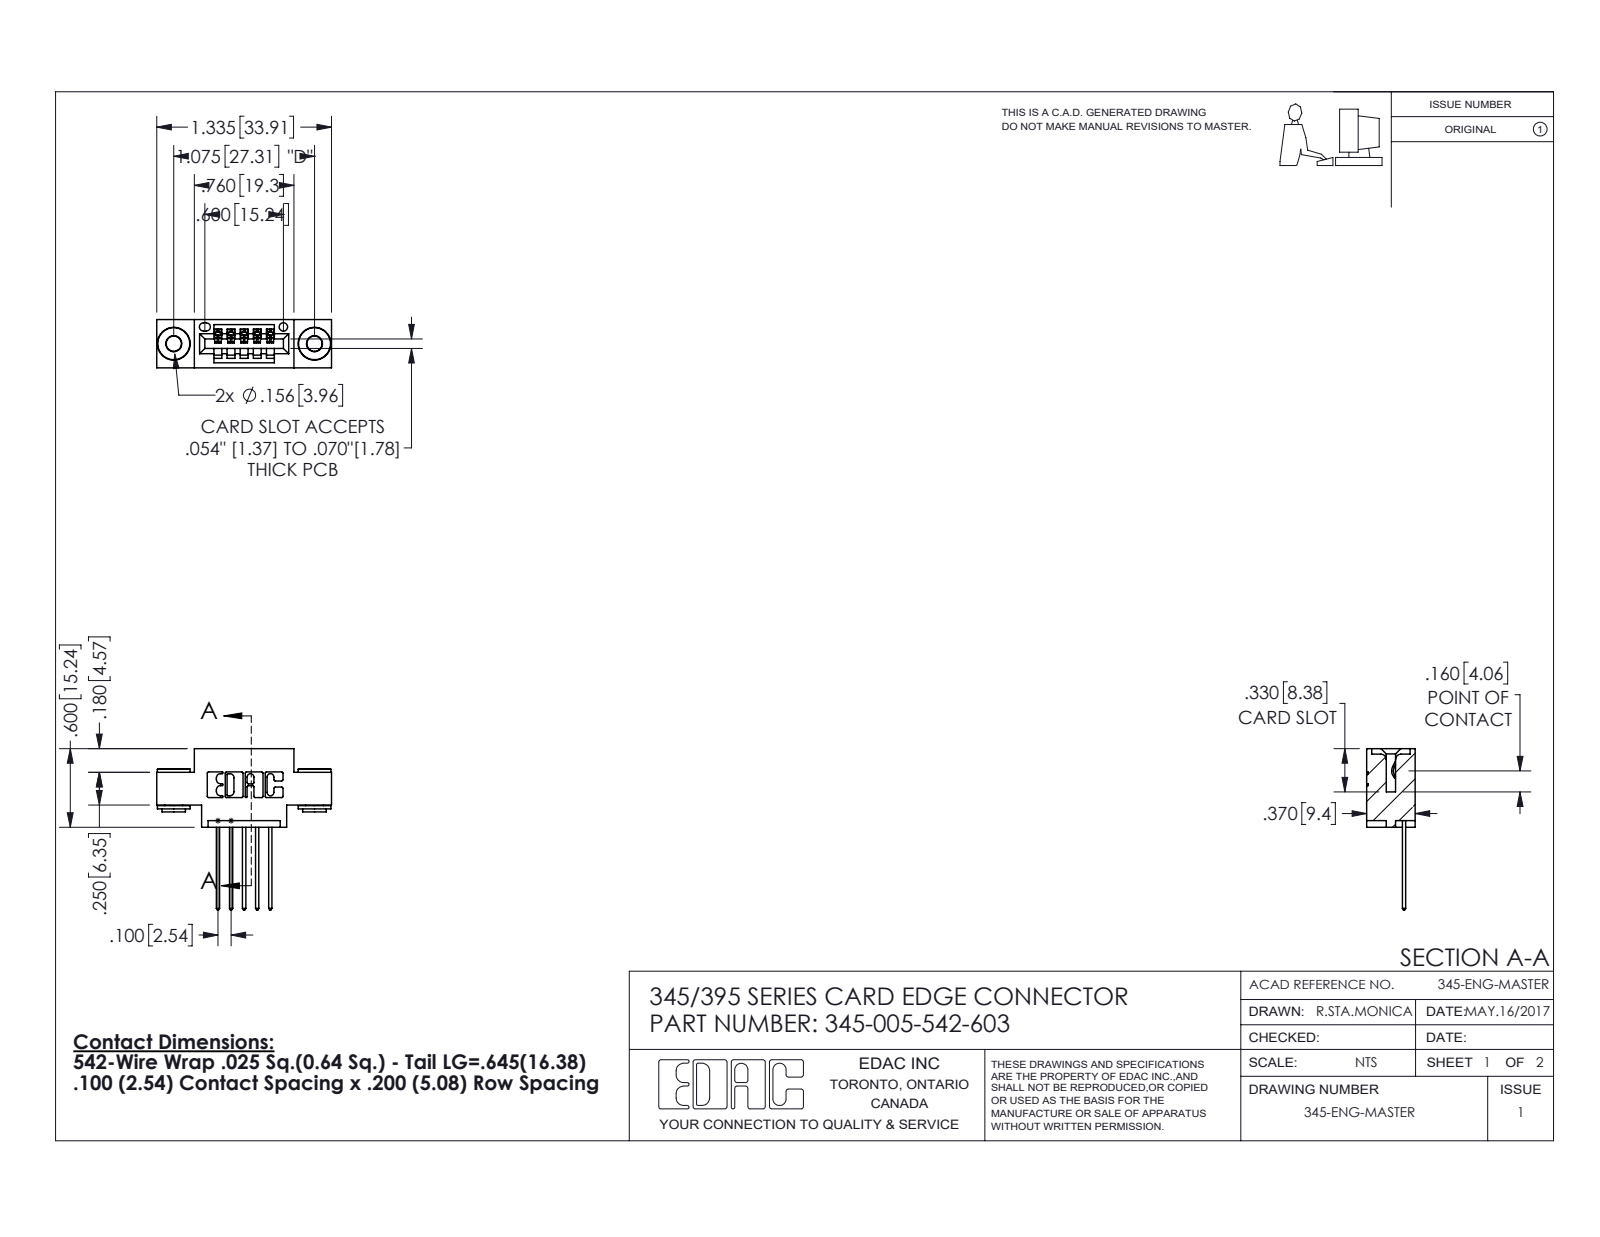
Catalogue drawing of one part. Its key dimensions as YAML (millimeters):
part_name: "345 Part_0.170 Offset - 0.156 Dia-TH; 345-005-542-603; 345-250-002_345-250-002-102; 345-292-001_345-293-142"
step_written_by: "SolidWorks 2016 (CONFIG_CONTROL_DESIGN)"
units: millimeters
bodies: {solids: 8, faces: 458, planar: 294, cylindrical: 156, other: 8}
overall_size: [33.9, 31.3, 9.4]
volume: 2830
surface_area: 3675
round_holes:
  - {diameter: 2.9, count: 2}
  - {diameter: 4, count: 2}
  - {diameter: 1.6, count: 1}
round_bosses_or_shafts:
  - {diameter: 6.4, count: 2}
  - {diameter: 4.6, count: 2}
  - {diameter: 3.5, count: 2}
partial_cylinders:
  - {radius: 0.3, count: 22}
  - {radius: 0.2, count: 10}
  - {radius: 0.3, count: 10}
  - {radius: 0.2, count: 6}
  - {radius: 0.8, count: 6}
  - {radius: 0.7, count: 3}
  - {radius: 0.8, count: 2}
  - {radius: 1, count: 2}
face_to_face_distances: [9.4, 5.1, 2.5, 1.8, 7.6, 0.6, 6.4, 2.5, 6.9, 1.5]
hole_center_spacings: [6.9, 21.5, 27.3]
